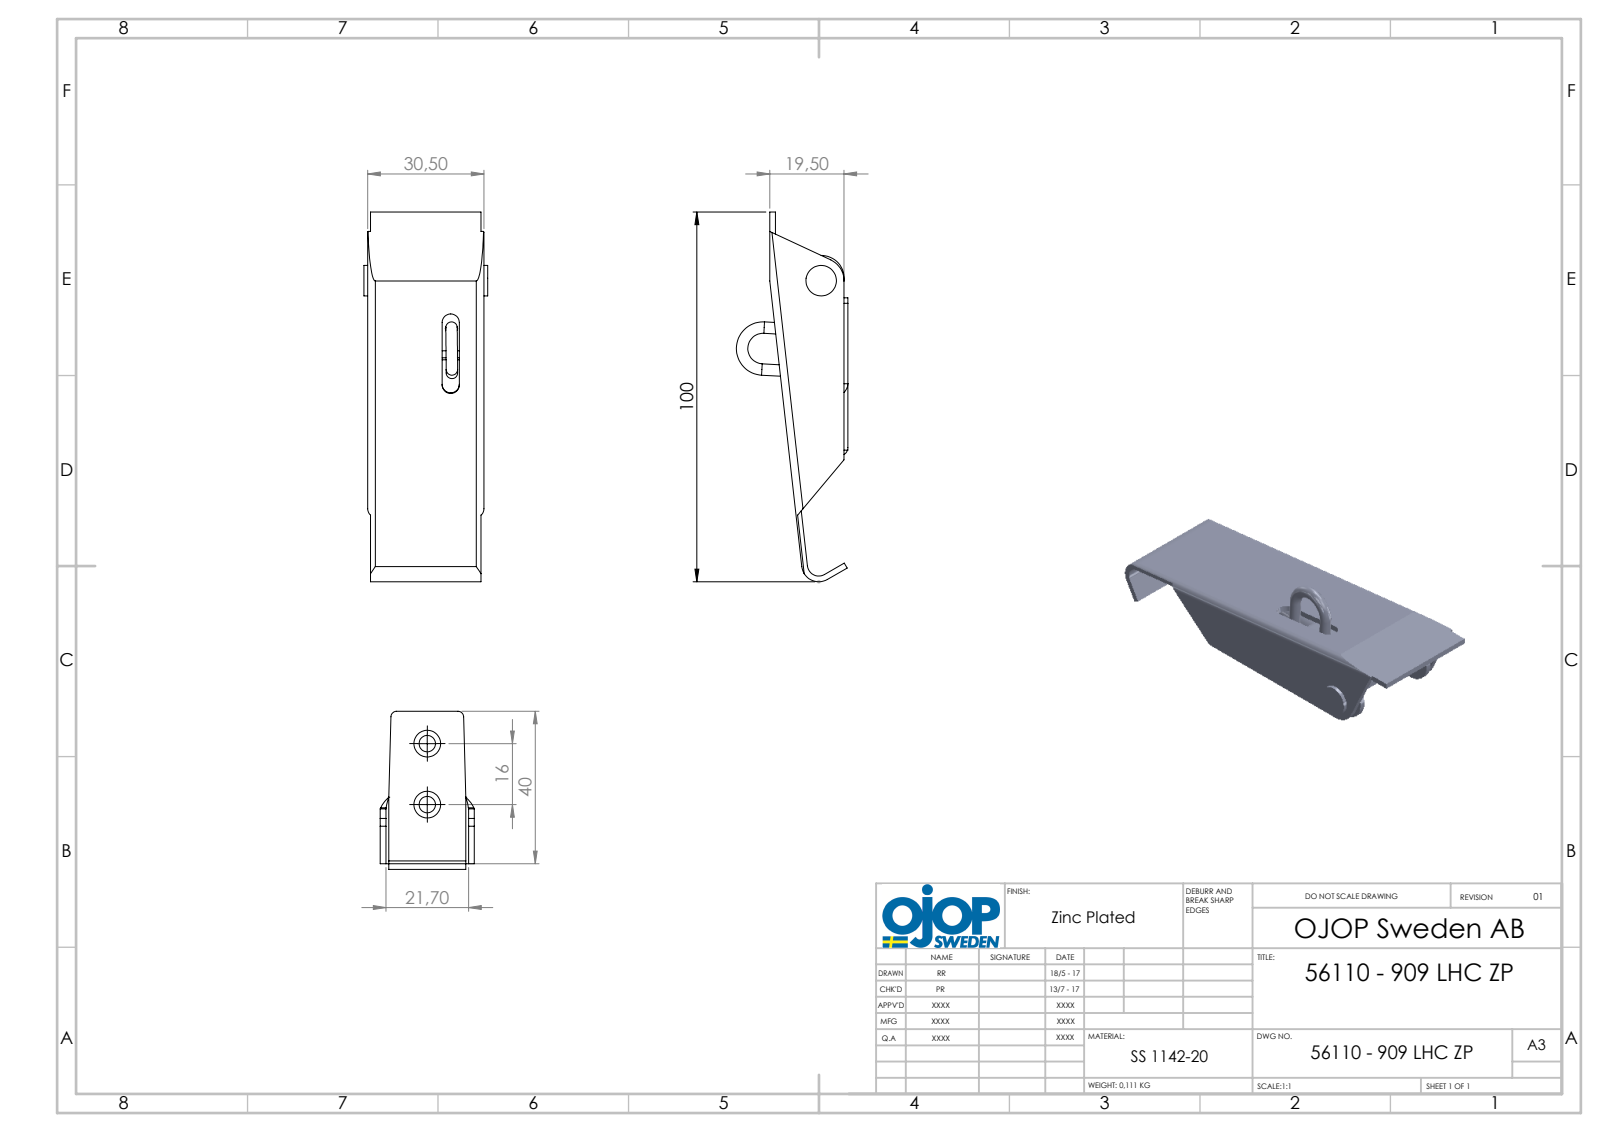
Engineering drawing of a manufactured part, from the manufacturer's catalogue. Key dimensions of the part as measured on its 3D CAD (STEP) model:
Part name (STEP PRODUCT): mellandel; 56110 - 909 LHC ZP; plastbit; underdel (+4 more)
STEP written by: SolidWorks 2015 (AUTOMOTIVE_DESIGN)
Units: millimetres
Bodies: 9 solids, 191 faces (89 planar, 86 cylindrical, 16 other)
Overall size (bounding box): 97 × 32.5 × 29.29
Volume: 15 257 mm³ · Surface area: 19 266 mm²
Round holes (diameter × count): ⌀4.3 ×2, ⌀3.2 ×1, ⌀4 ×1, ⌀4.1 ×1, ⌀5 ×1, ⌀5.3 ×1, ⌀6 ×1
Round bosses / shafts (diameter × count): ⌀3 ×2, ⌀10 ×1, ⌀8 ×1, ⌀7 ×1, ⌀6 ×1, ⌀3.9 ×1
Partial cylindrical surfaces — rounded edges, fillets, slot ends (radius × count): R2 ×7, R1 ×4, R0.74 ×3, R2.24 ×3, R1.5 ×2, R2.25 ×2, R3 ×2, R6 ×2
Main face-to-face distances: 1.5, 29, 19.02, 27.5, 30.5, 2.5, 27, 26.5, 2, 24.5
Hole centre spacings: 16, 39.65
